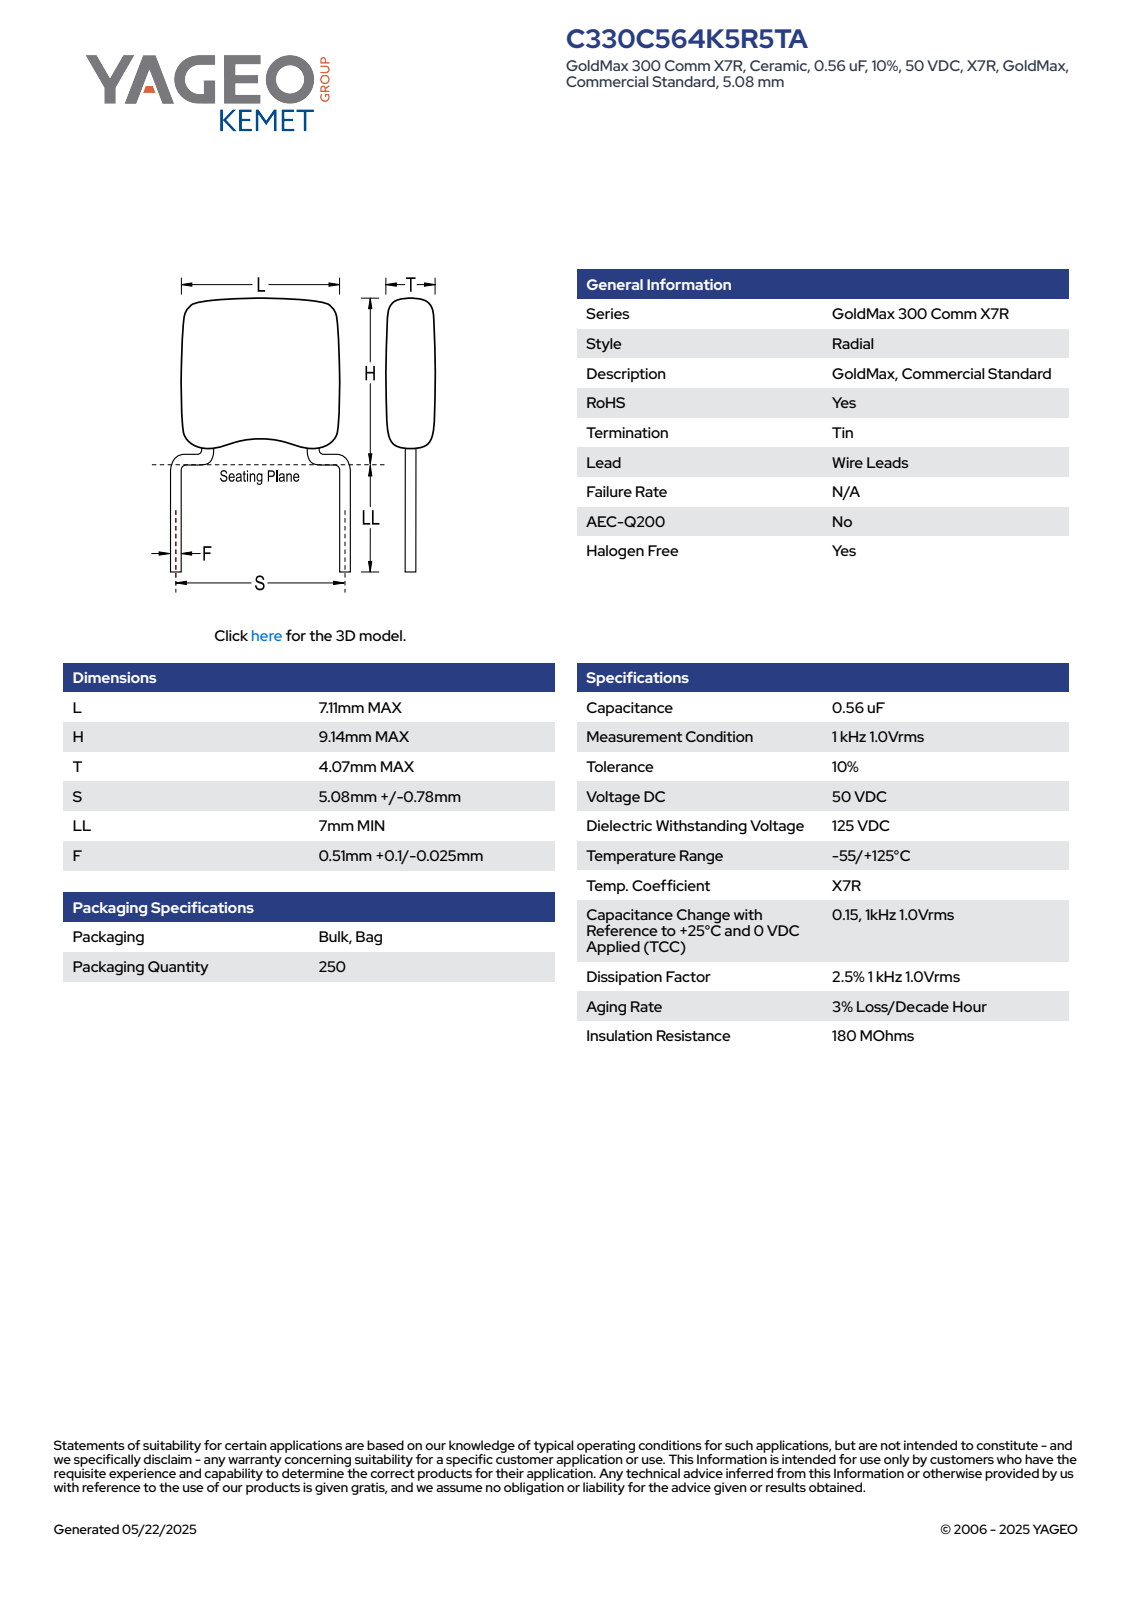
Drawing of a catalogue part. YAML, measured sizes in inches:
part_name: "CCR_SB_7.11X10.16_L7.11H10.16T4.07S5.08LL7F0.61"
step_written_by: "SolidWorks 2021 (AUTOMOTIVE_DESIGN)"
units: inches
bodies: {solids: 4, faces: 97, planar: 65, cylindrical: 14, other: 18}
overall_size: [0.676, 0.28, 0.161]
volume: 0.012
surface_area: 0.349
round_bosses_or_shafts:
  - {diameter: 0.024, count: 2}
partial_cylinders:
  - {radius: 0.039, count: 10}
face_to_face_distances: [0.16, 0.28, 0.265, 0.161, 0.145, 0.12, 0.122, 0.024, 0.143, 0.024]
